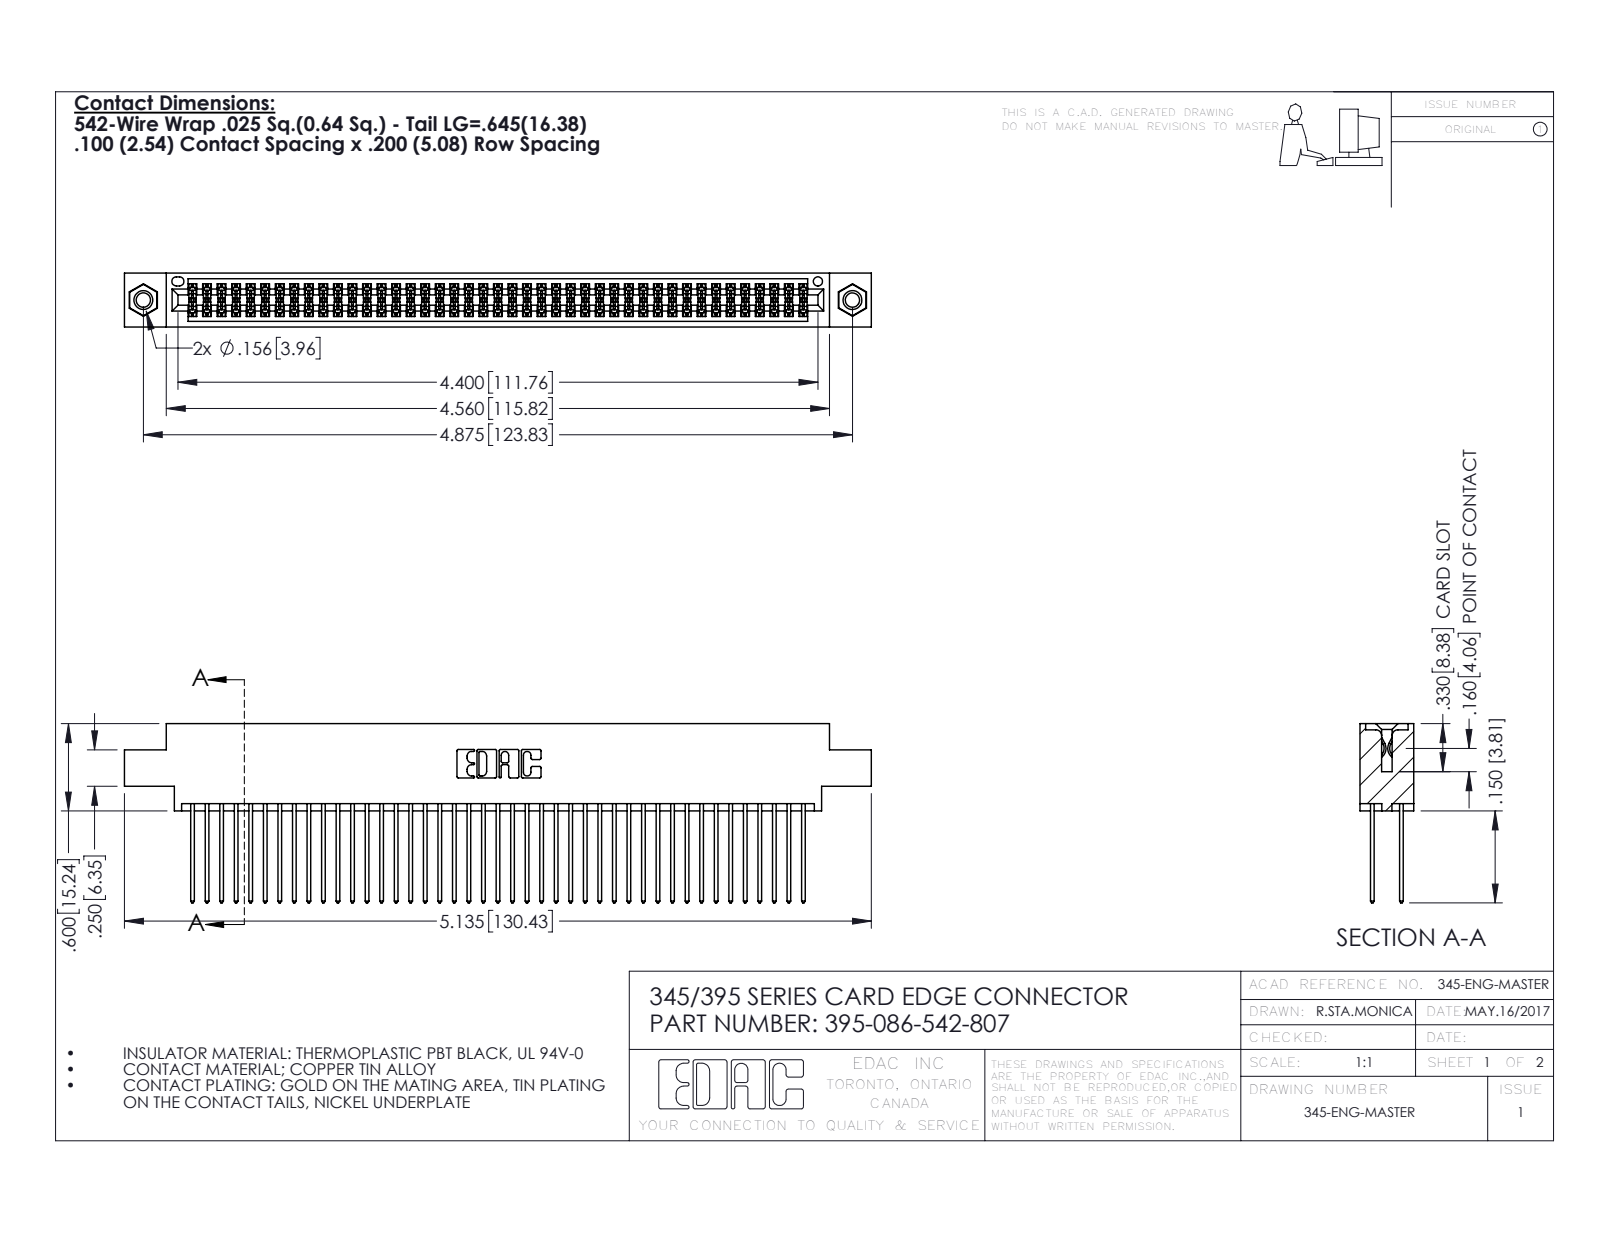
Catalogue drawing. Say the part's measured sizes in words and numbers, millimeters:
The part is named "345-250-001_345-250-005-103; 345 Part_0.170 Offset - 0.156 Dia-TI; 345-292-001_345-293-142; 395-086-542-807". Its 3-D file was written by "SolidWorks 2016 (CONFIG_CONTROL_DESIGN)". It is 89 solids with 4490 faces: 2954 planar, 1520 cylindrical and 16 other. Overall it measures 130.4 by 31.3 by 9.4 millimeters. Its volume is 12 900 cubic millimeters and its surface area 21 210 square millimeters. Round holes: 2 of diameter 2.5, 2 of diameter 3.2, 2 of diameter 4, 1 of diameter 1.6. Round bosses or shafts: 2 of diameter 3.9. Partial cylindrical surfaces (rounded edges, fillets, slot ends): 129 of radius 0.2, 86 of radius 0.3, 22 of radius 0.3, 6 of radius 0.2, 6 of radius 0.8, 3 of radius 0.7, 2 of radius 0.4, 2 of radius 0.5. The main face-to-face distances are 1.8, 7.6, 5.1, 2.5, 6.9, 0.6, 9.4, 5.7, 4.4, 3.8. The hole center spacings are 6.9, 117.8, 123.8.
